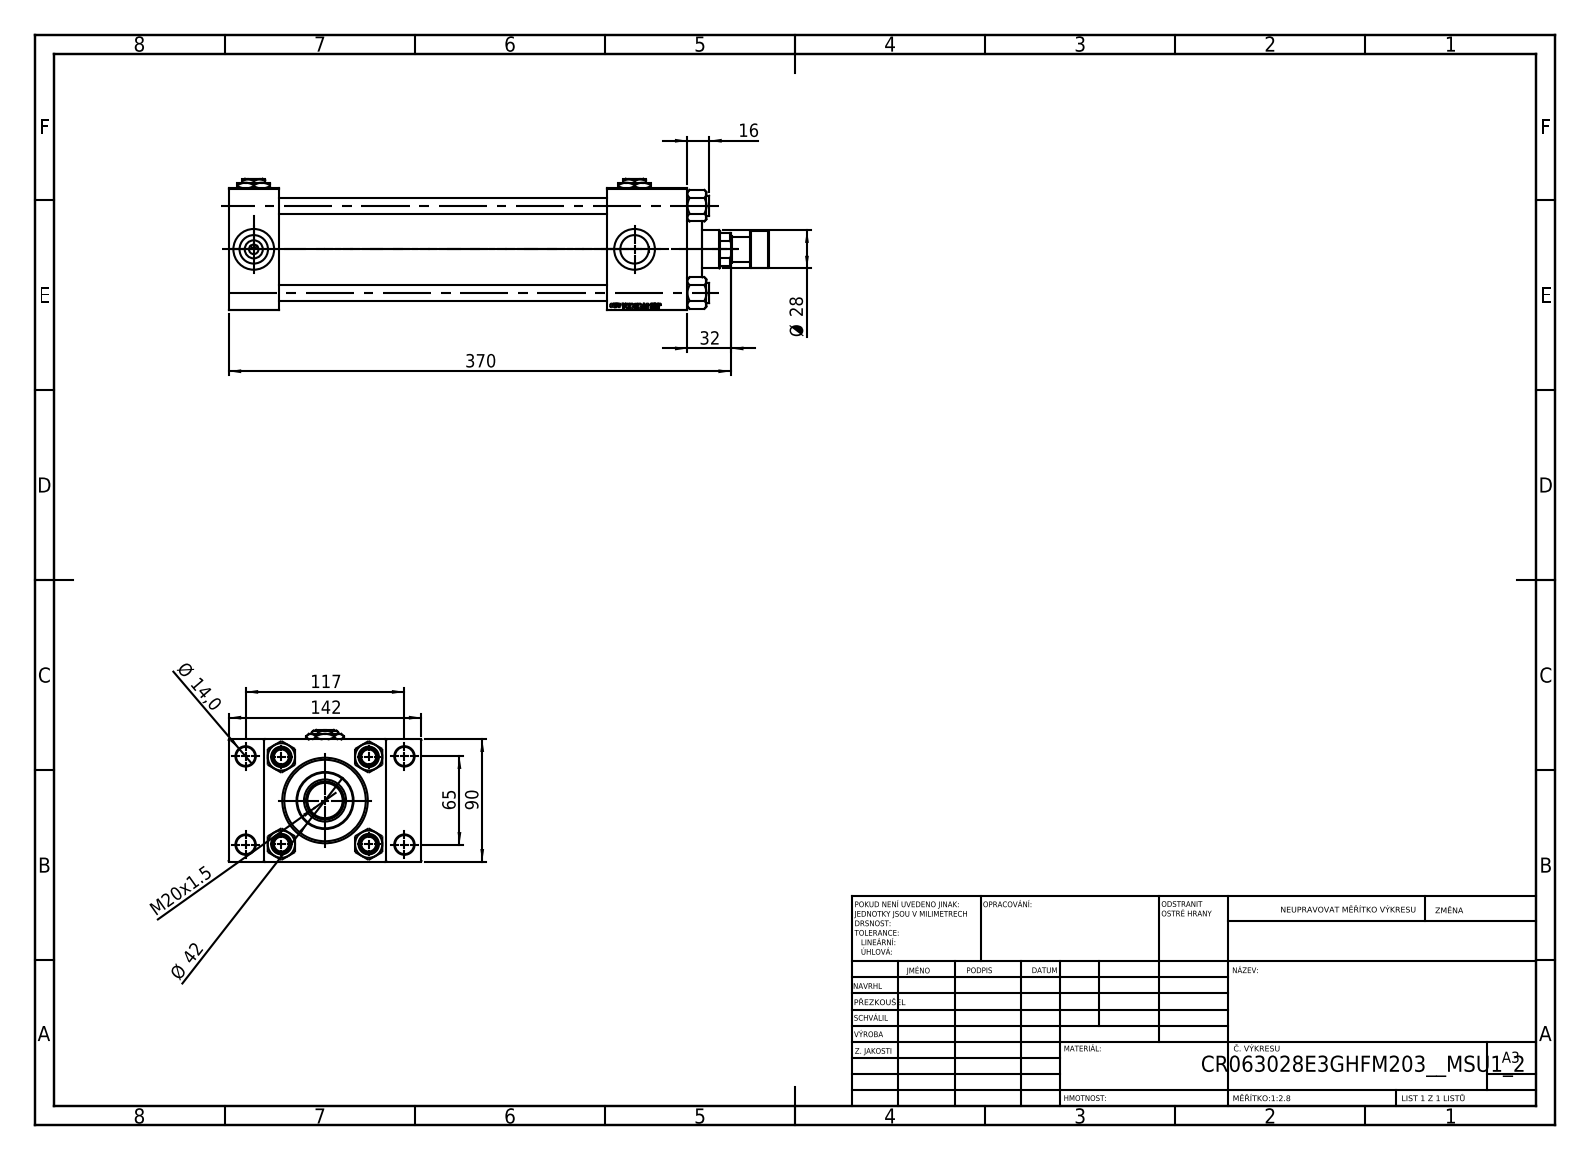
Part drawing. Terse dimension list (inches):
name: V215_VC_A; V215CR_TYCINKA_E; V215CR_E_Body; V215CR_ROD_END_F (+3 more)
written by: SolidWorks 2019 (CONFIG_CONTROL_DESIGN)
unit: in
bodies: 14 solids, 1251 faces (550 planar, 101 cylindrical, 600 other)
size: 15.669 × 5.591 × 3.819
volume: 86.59 in³; area: 518.1 in²
holes: 4× ⌀0.472, 4× ⌀0.551, 4× ⌀0.825, 4× ⌀1.181, 3× ⌀0.276, 1× ⌀0.728, 1× ⌀1.102, 1× ⌀1.22, 1× ⌀1.969, 1× ⌀2.362, 1× ⌀2.48
bosses: 4× ⌀0.591, 1× ⌀2.717, 1× ⌀1.654, 1× ⌀1.063, 1× ⌀0.709
face distances: 3.543, 1.457, 13.307, 11.85, 1.024, 4.567, 2.323, 10.984, 9.528, 12.177
hole spacings: 1.037, 1.79, 2.531, 2.635, 2.748, 3.569, 4.383, 2.559
